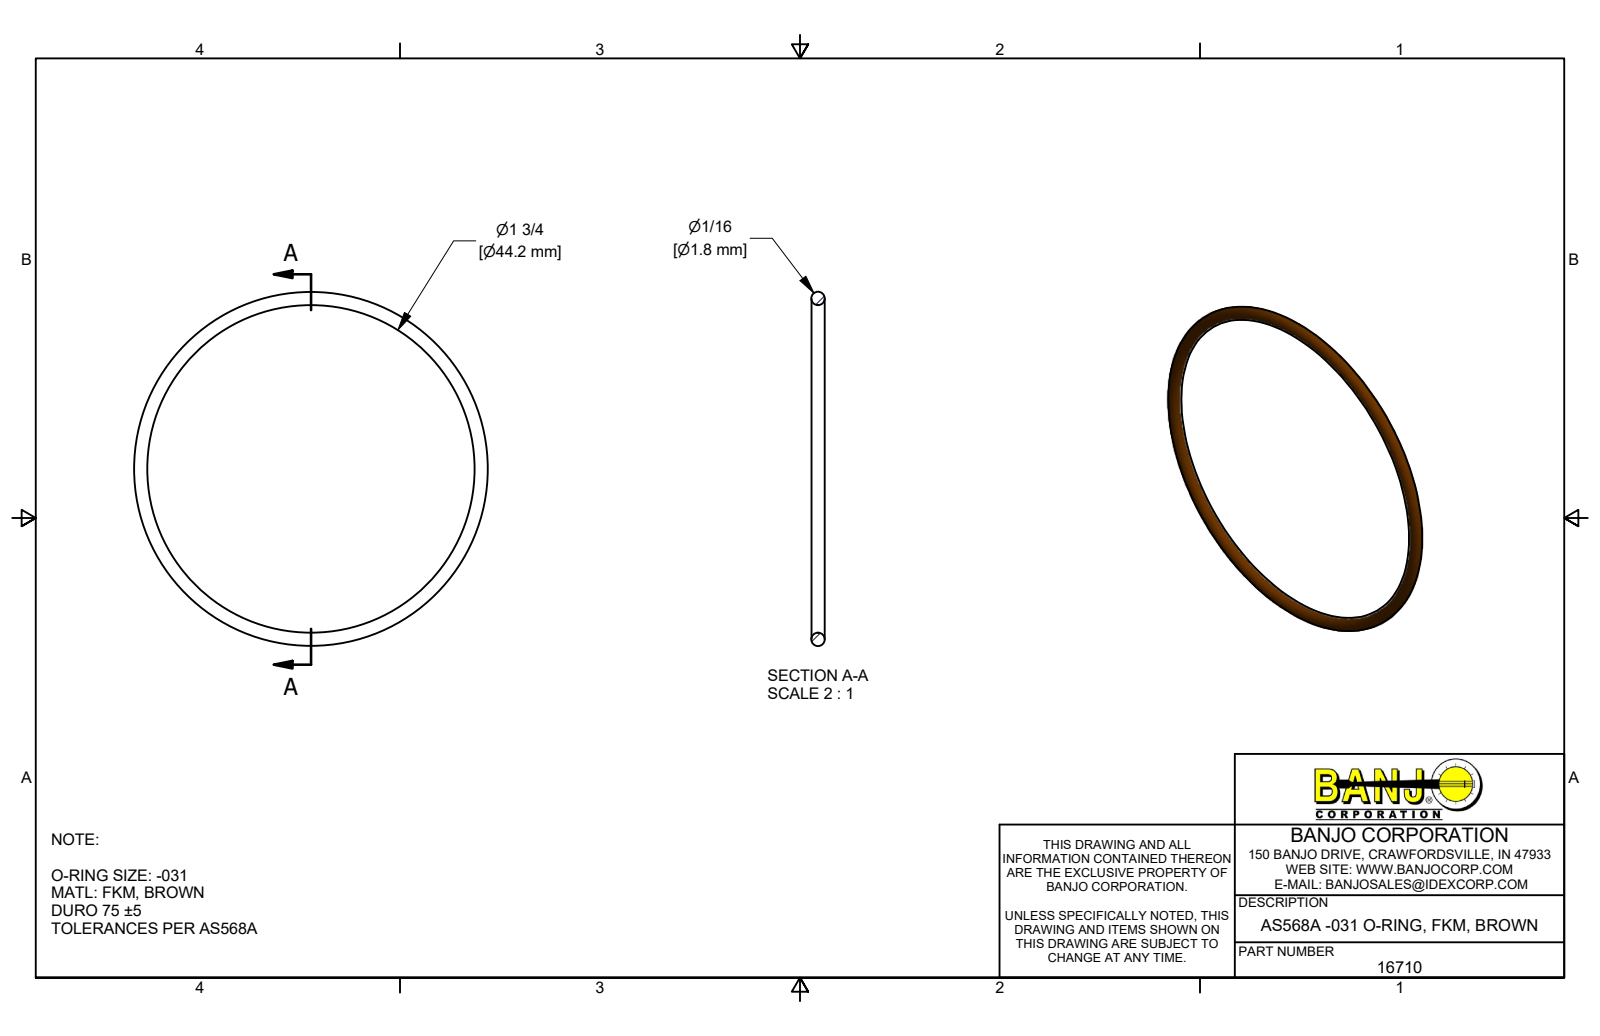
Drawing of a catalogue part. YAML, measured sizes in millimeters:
part_name: "16710"
step_written_by: "Autodesk Inventor 2019 (AUTOMOTIVE_DESIGN)"
units: millimeters
bodies: {solids: 1, faces: 1, planar: 0, cylindrical: 0, other: 1}
overall_size: [47.7, 47.7, 1.8]
volume: 360
surface_area: 806
